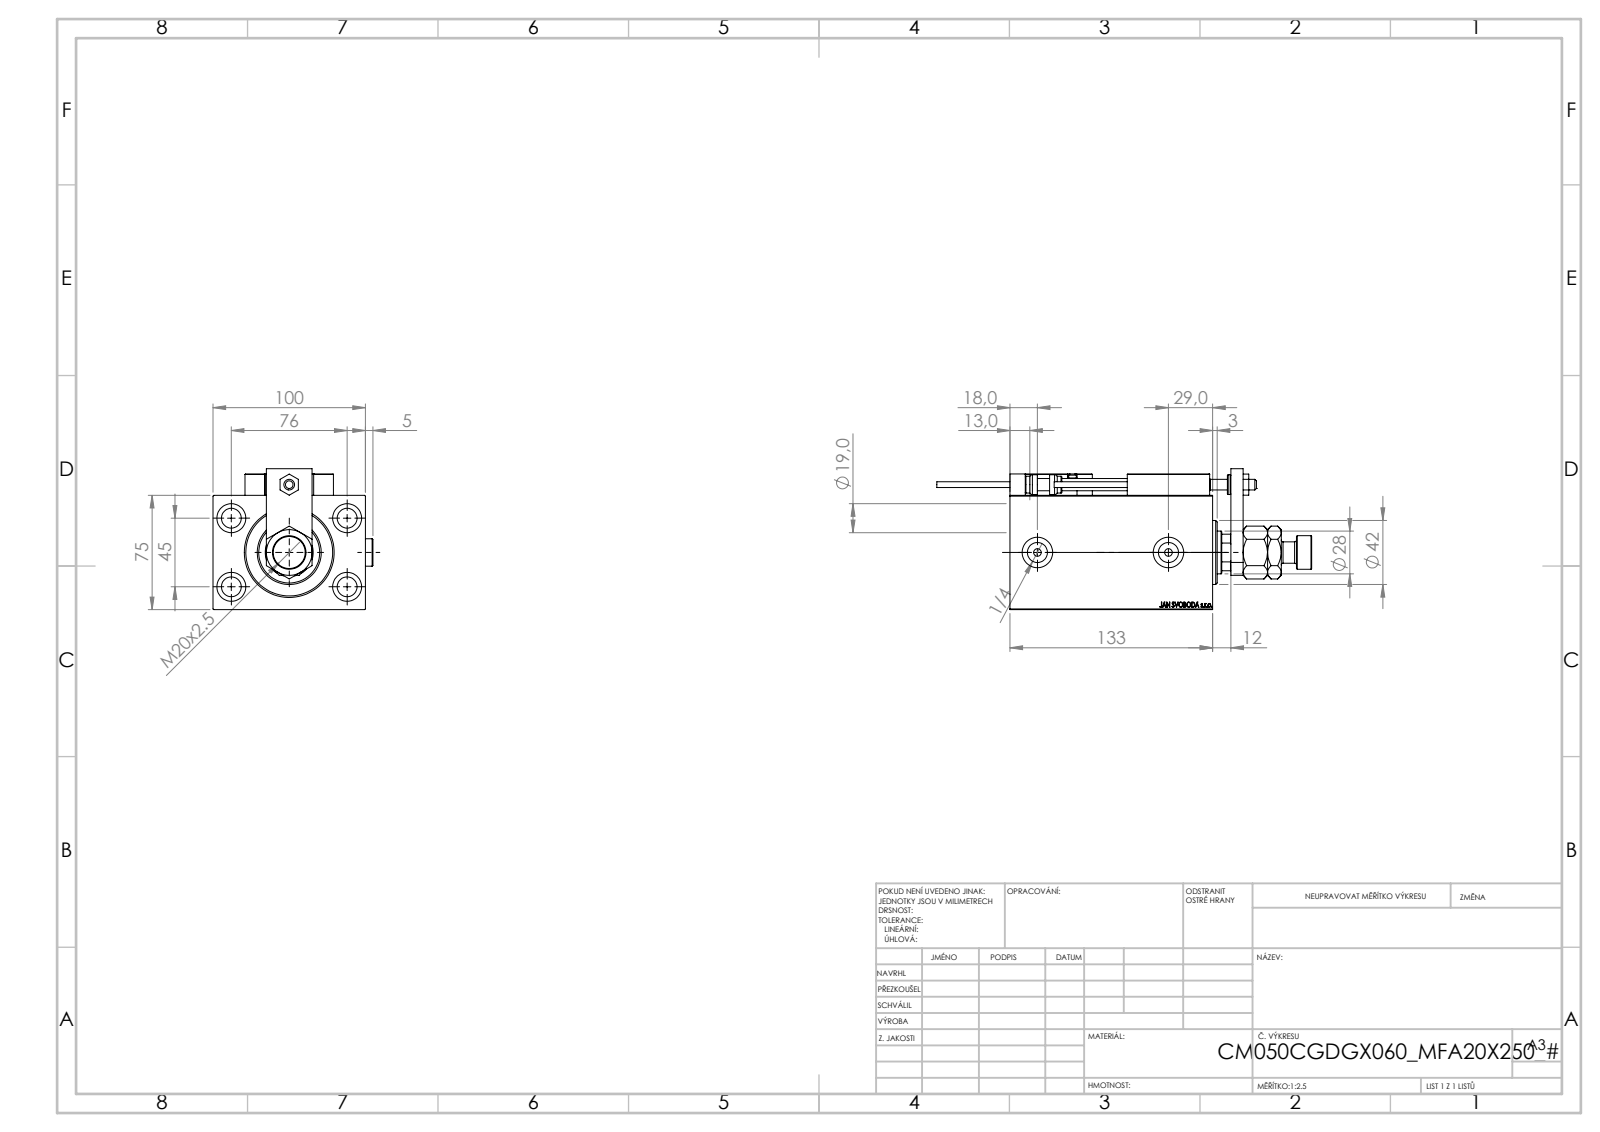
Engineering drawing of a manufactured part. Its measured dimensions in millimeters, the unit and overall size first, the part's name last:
Units: millimetres
Overall size (bounding box): 246 × 104.9 × 92.5
Round holes (diameter × count): ⌀8 ×5, ⌀3.2 ×4, ⌀4 ×4, ⌀5 ×4, ⌀13 ×4, ⌀19 ×4, ⌀20 ×3, ⌀13.16 ×2, ⌀7 ×1, ⌀18.5 ×1, ⌀28 ×1, ⌀31.5 ×1
Round bosses / shafts (diameter × count): ⌀18 ×2, ⌀5 ×2, ⌀3.8 ×2, ⌀42 ×1, ⌀22 ×1, ⌀14 ×1, ⌀13 ×1, ⌀11 ×1
Partial cylindrical surfaces — rounded edges, fillets, slot ends (radius × count): R0.3 ×30, R3 ×2, R13.5 ×1
Main face-to-face distances: 75, 100, 14, 133, 12, 119, 20, 8, 24, 25
Hole centre spacings: 44.16, 11.37, 20, 29.59, 29.69, 36.06, 42.19, 43.91
Volume: 907 809 mm³ · Surface area: 168 202 mm²
Bodies: 26 solids, 1391 faces (611 planar, 210 cylindrical, 570 other)
Part name (STEP PRODUCT): TYC_L79; SWITCH_X_FRONT_BACK; X_Y_MFA; Zatka_OIL_PORT (+7 more)
STEP written by: SolidWorks 2019 (CONFIG_CONTROL_DESIGN)
